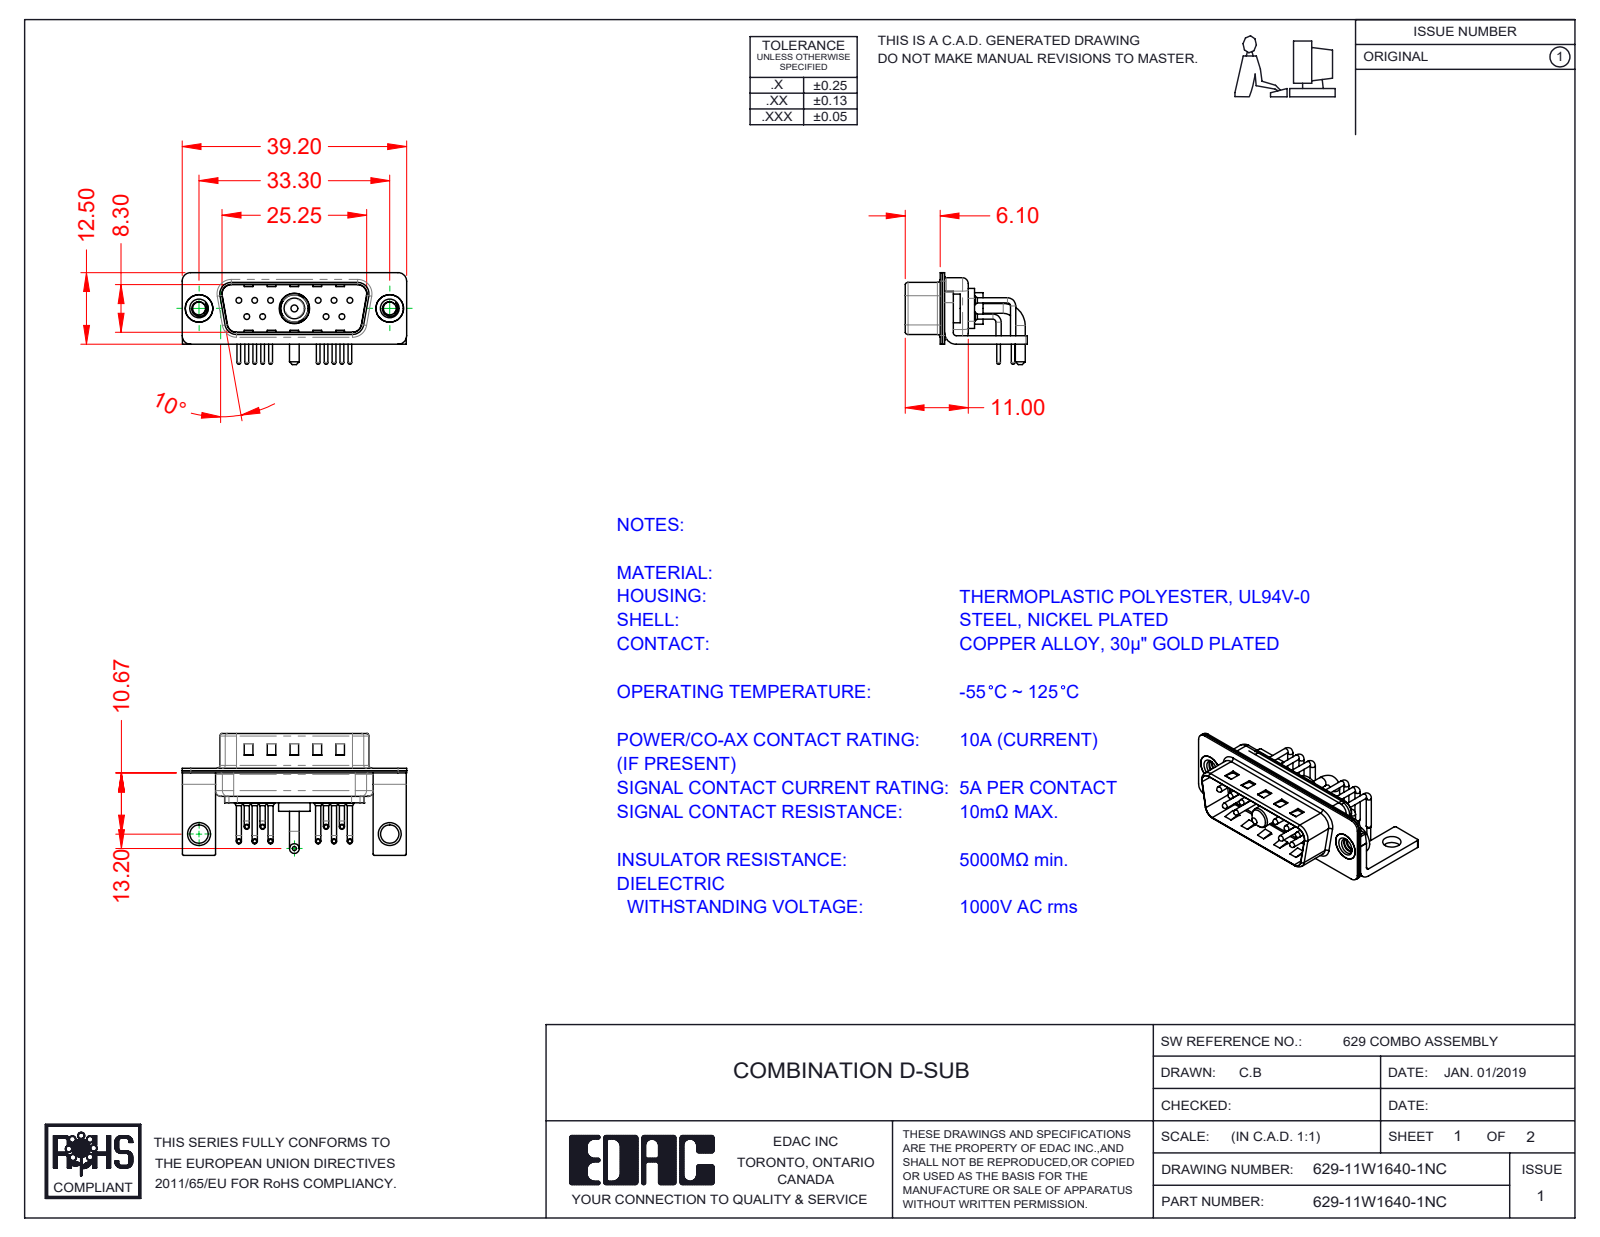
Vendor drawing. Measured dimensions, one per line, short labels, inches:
name: 629Combo Threaded Rivet_2; 629Combo Housing_11W1; 629Combo Contact Row 1; 629Combo Shell Rear_15 Contacts (+5 more)
written by: SolidWorks 2020 (CONFIG_CONTROL_DESIGN)
unit: in
bodies: 19 solids, 1544 faces (818 planar, 542 cylindrical, 184 other)
size: 1.543 × 0.839 × 0.632
volume: 0.141 in³; area: 9.029 in²
holes: 10× ⌀0.03, 10× ⌀0.063, 10× ⌀0.079, 2× ⌀0.089, 2× ⌀0.126, 2× ⌀0.157, 2× ⌀0.189, 1× ⌀0.191, 1× ⌀0.209
bosses: 20× ⌀0.035, 10× ⌀0.059, 10× ⌀0.039, 10× ⌀0.026, 2× ⌀0.197, 2× ⌀0.193, 2× ⌀0.067, 1× ⌀0.217
rounds: 16× R0.01, 16× R0.059, 13× R0.079, 10× R0.04, 9× R0.02, 8× R0.063, 7× R0.039, 4× R0.024
face distances: 0.016, 0.031, 0.059, 0.374, 0.358, 0.024, 0.343, 0.39, 0.047, 0.205
hole spacings: 0.124, 0.109, 0.545, 0.436, 0.654, 0.198, 0.198, 0.218
